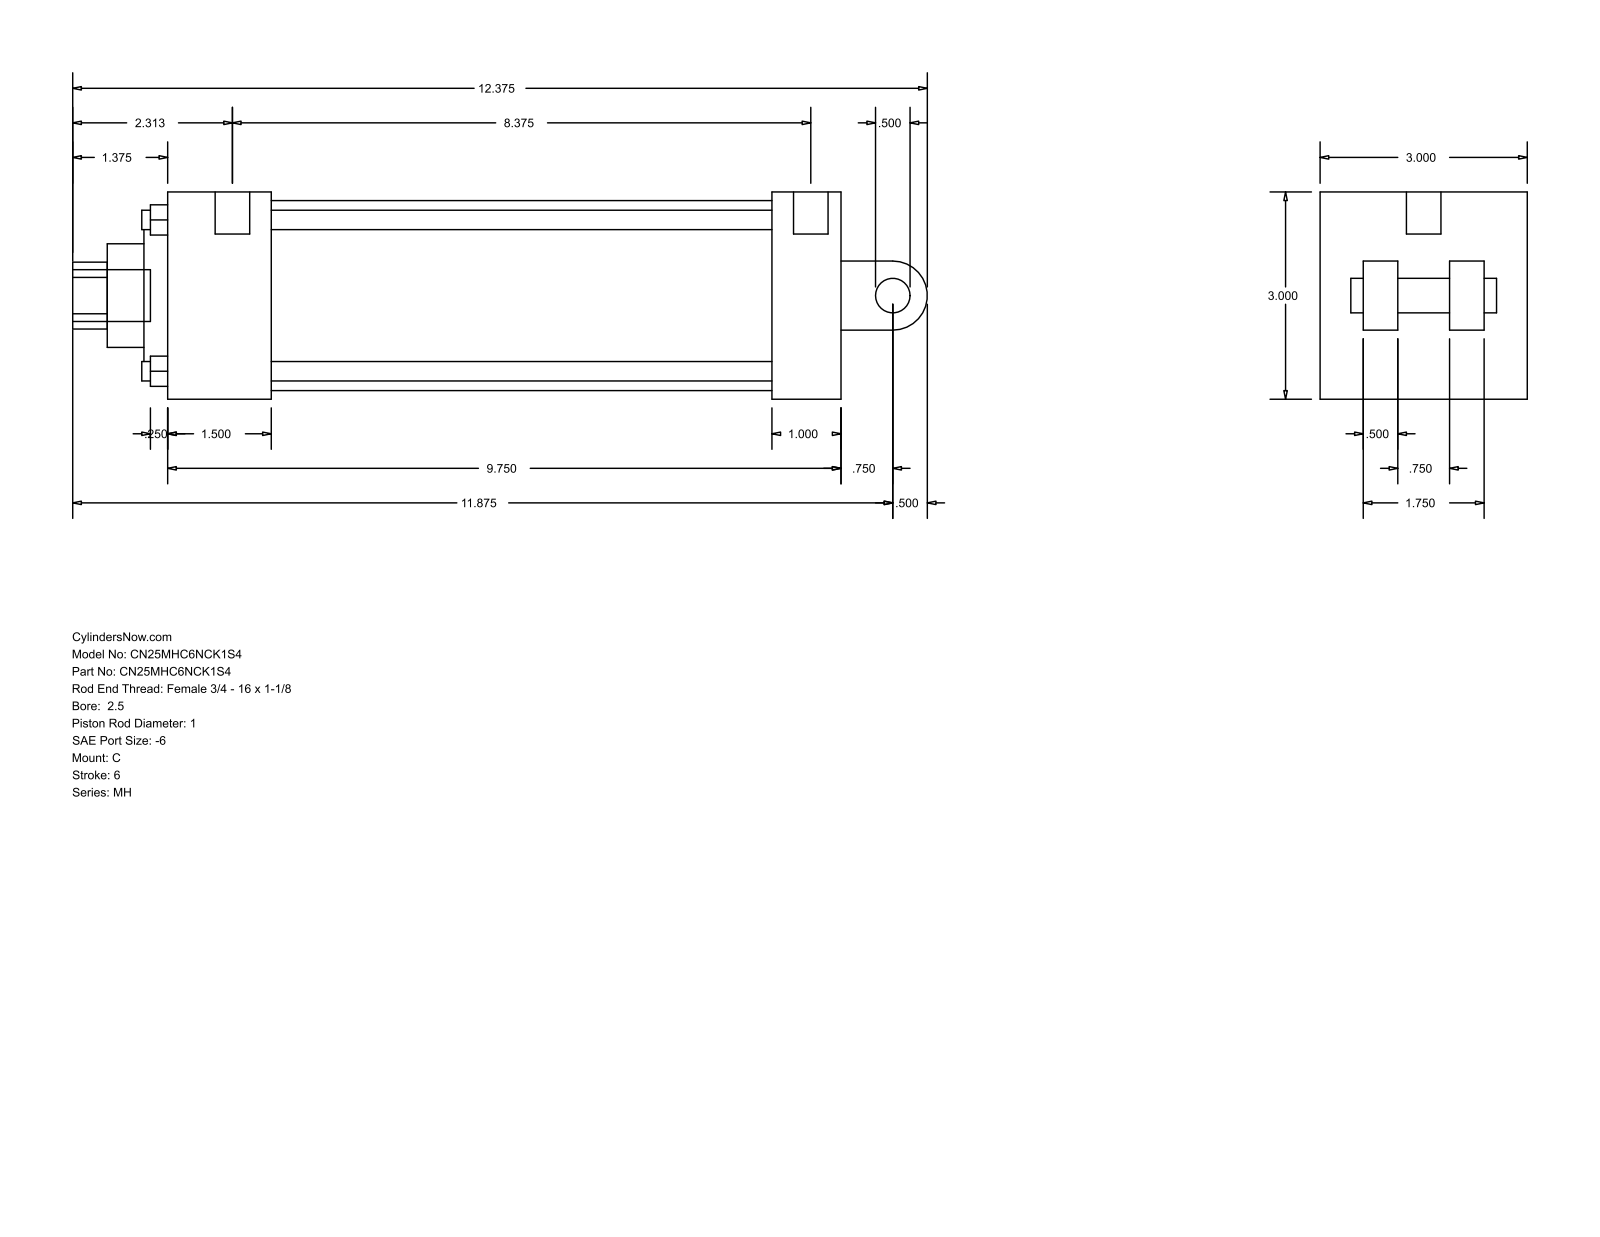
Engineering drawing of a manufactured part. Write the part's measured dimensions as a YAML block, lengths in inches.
part_name: "MH_C__0250_1"
step_written_by: "GSSL Pune (CONFIG_CONTROL_DESIGN)"
units: inches
bodies: {solids: 0, faces: 101, planar: 71, cylindrical: 30, other: 0}
overall_size: [12.375, 3, 3]
round_holes:
  - {diameter: 0.281, count: 4}
  - {diameter: 0.219, count: 2}
  - {diameter: 0.5, count: 1}
  - {diameter: 1, count: 1}
  - {diameter: 1.5, count: 1}
  - {diameter: 2.375, count: 1}
  - {diameter: 2.75, count: 1}
round_bosses_or_shafts:
  - {diameter: 0.5, count: 2}
  - {diameter: 0.219, count: 2}
  - {diameter: 0.75, count: 1}
partial_cylinders:
  - {radius: 0.484, count: 1}
  - {radius: 0.5, count: 1}
face_to_face_distances: [3, 9.75, 0.625, 1, 2.375, 8.75, 1.5, 7.25, 8.25, 0.5]
hole_center_spacings: [1.548, 2.19, 3.097, 0.125]
